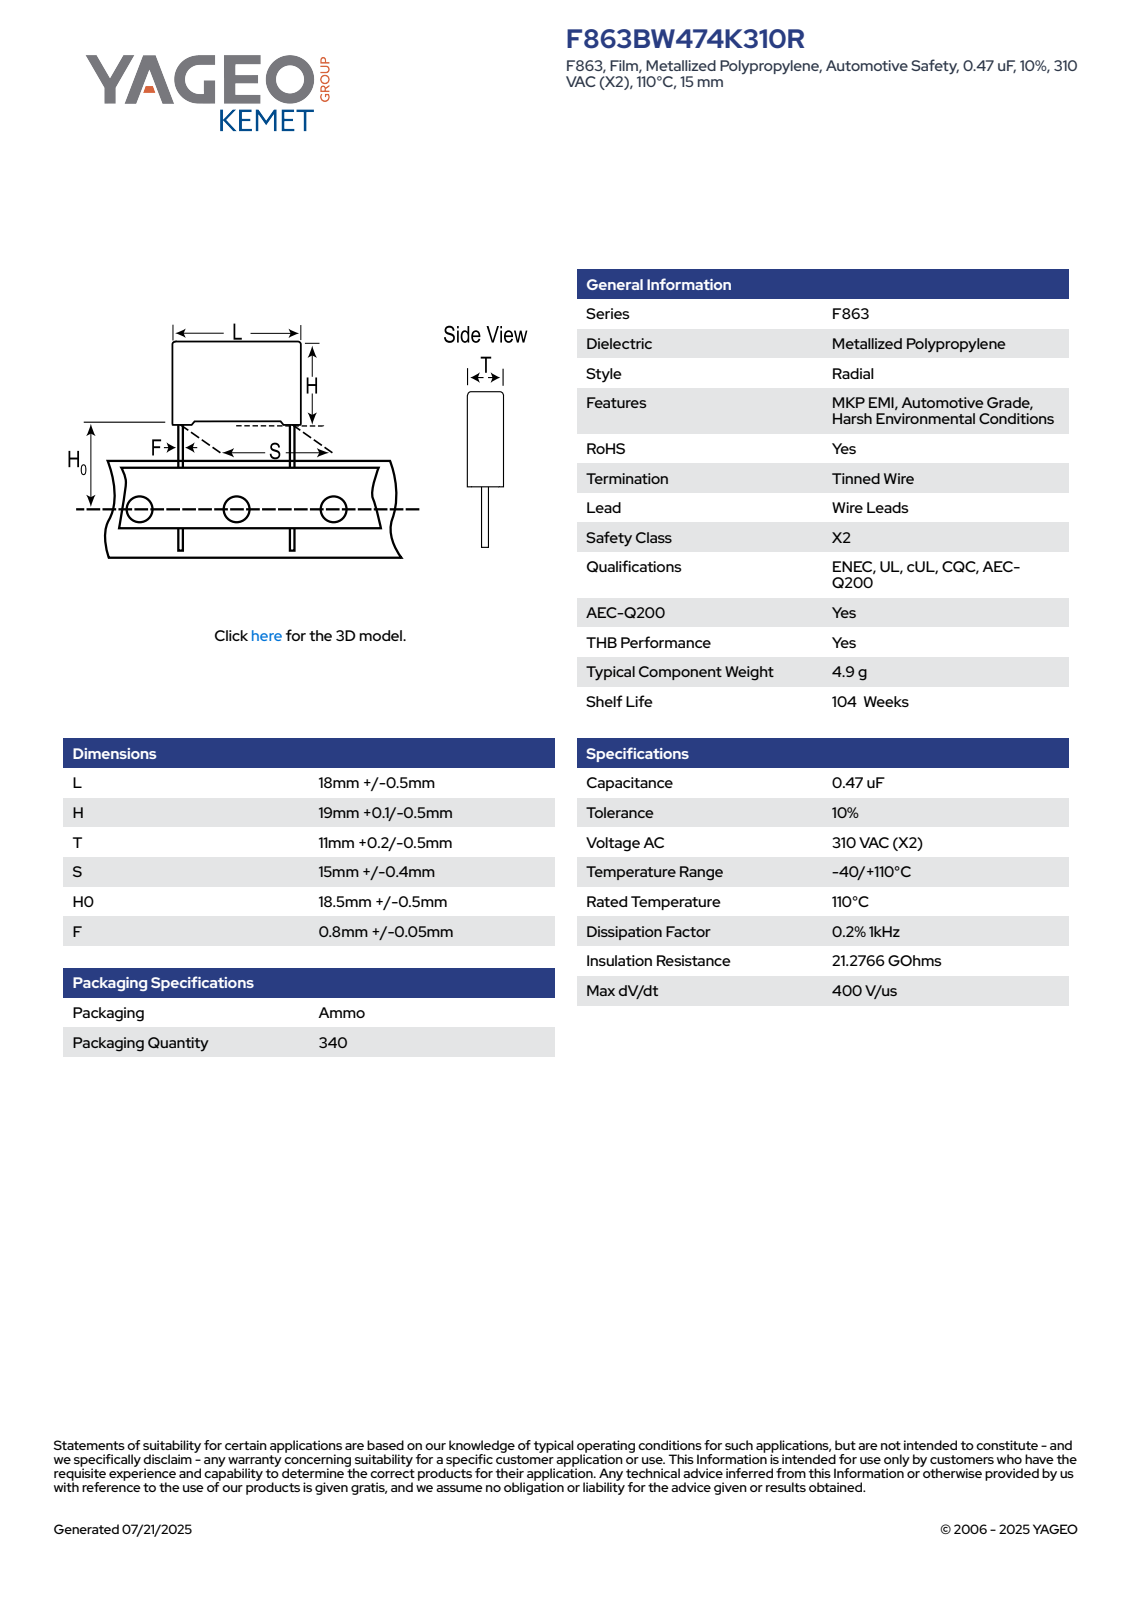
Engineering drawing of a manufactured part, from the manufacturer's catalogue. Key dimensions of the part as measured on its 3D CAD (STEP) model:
Part name (STEP PRODUCT): CFR_RB_18X19X11_L18.3H19.1T11.2S15LL19F0.85
STEP written by: SolidWorks 2014 (AUTOMOTIVE_DESIGN)
Units: millimetres
Bodies: 4 solids, 89 faces (81 planar, 8 cylindrical, 0 other)
Overall size (bounding box): 38.1 × 18.3 × 11.21
Volume: 3 760 mm³ · Surface area: 1 619 mm²
Round bosses / shafts (diameter × count): ⌀0.85 ×2
Partial cylindrical surfaces — rounded edges, fillets, slot ends (radius × count): R0.69 ×4
Main face-to-face distances: 11.2, 18.3, 18.24, 11.21, 0.6, 10.6, 0.86, 19.1, 0.61, 10
